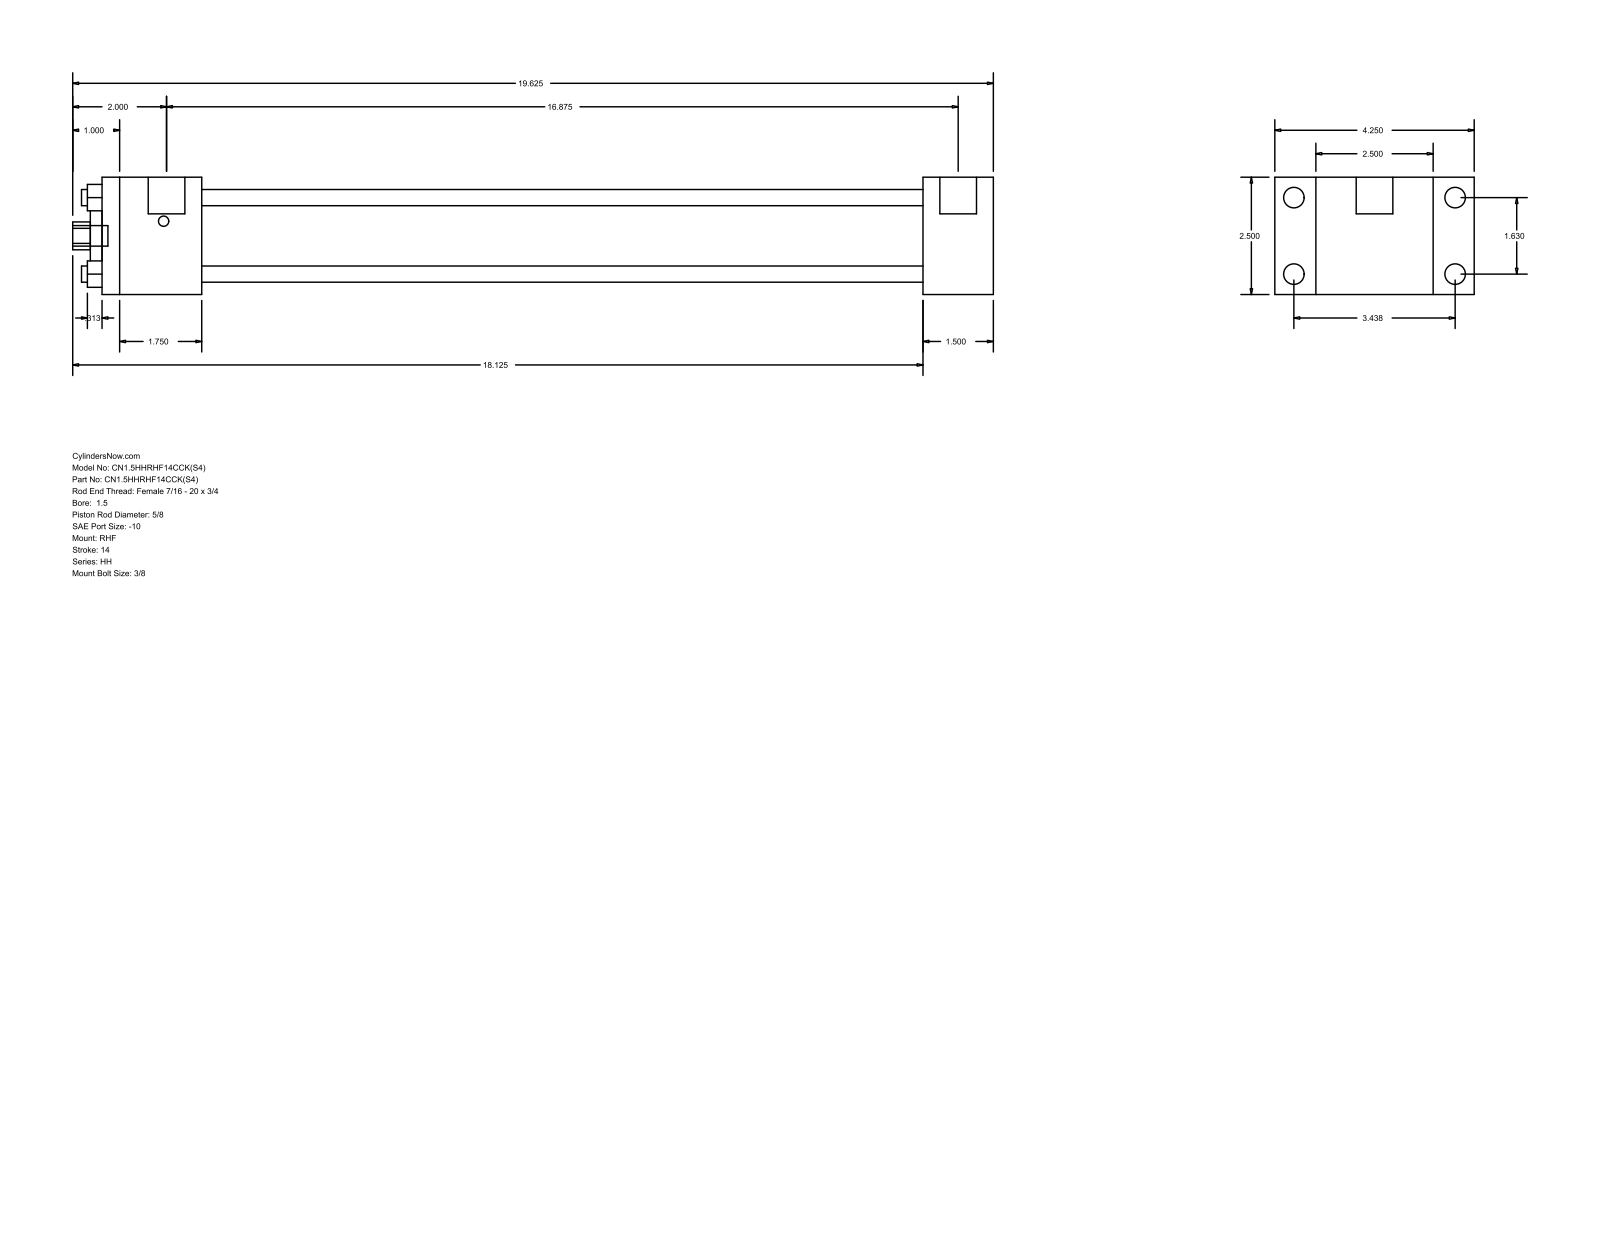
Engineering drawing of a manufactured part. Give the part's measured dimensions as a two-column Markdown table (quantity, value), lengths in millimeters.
| quantity | value |
| --- | --- |
| part name | HH_RHF__0150_0.625 |
| STEP written by | GSSL Pune (CONFIG_CONTROL_DESIGN) |
| units | millimeters |
| bodies | 0 solids, 88 faces (60 planar, 28 cylindrical, 0 other) |
| overall size | 498.48 × 107.95 × 63.5 |
| round holes (diameter × count) | 8.76 × 4, 15.88 × 1, 28.57 × 1, 44.45 × 1 |
| round bosses / shafts (diameter × count) | 11.13 × 4, 5.56 × 4, 19.84 × 2, 11.11 × 1 |
| partial cylindrical surfaces (radius × count) | 7.54 × 1 |
| main face-to-face distances | 63.5, 38.1, 22.23, 85.73, 444.5, 482.6, 107.96, 53.97, 390.53, 428.63 |
| hole center spacings | 29.27, 41.4, 58.55 |
